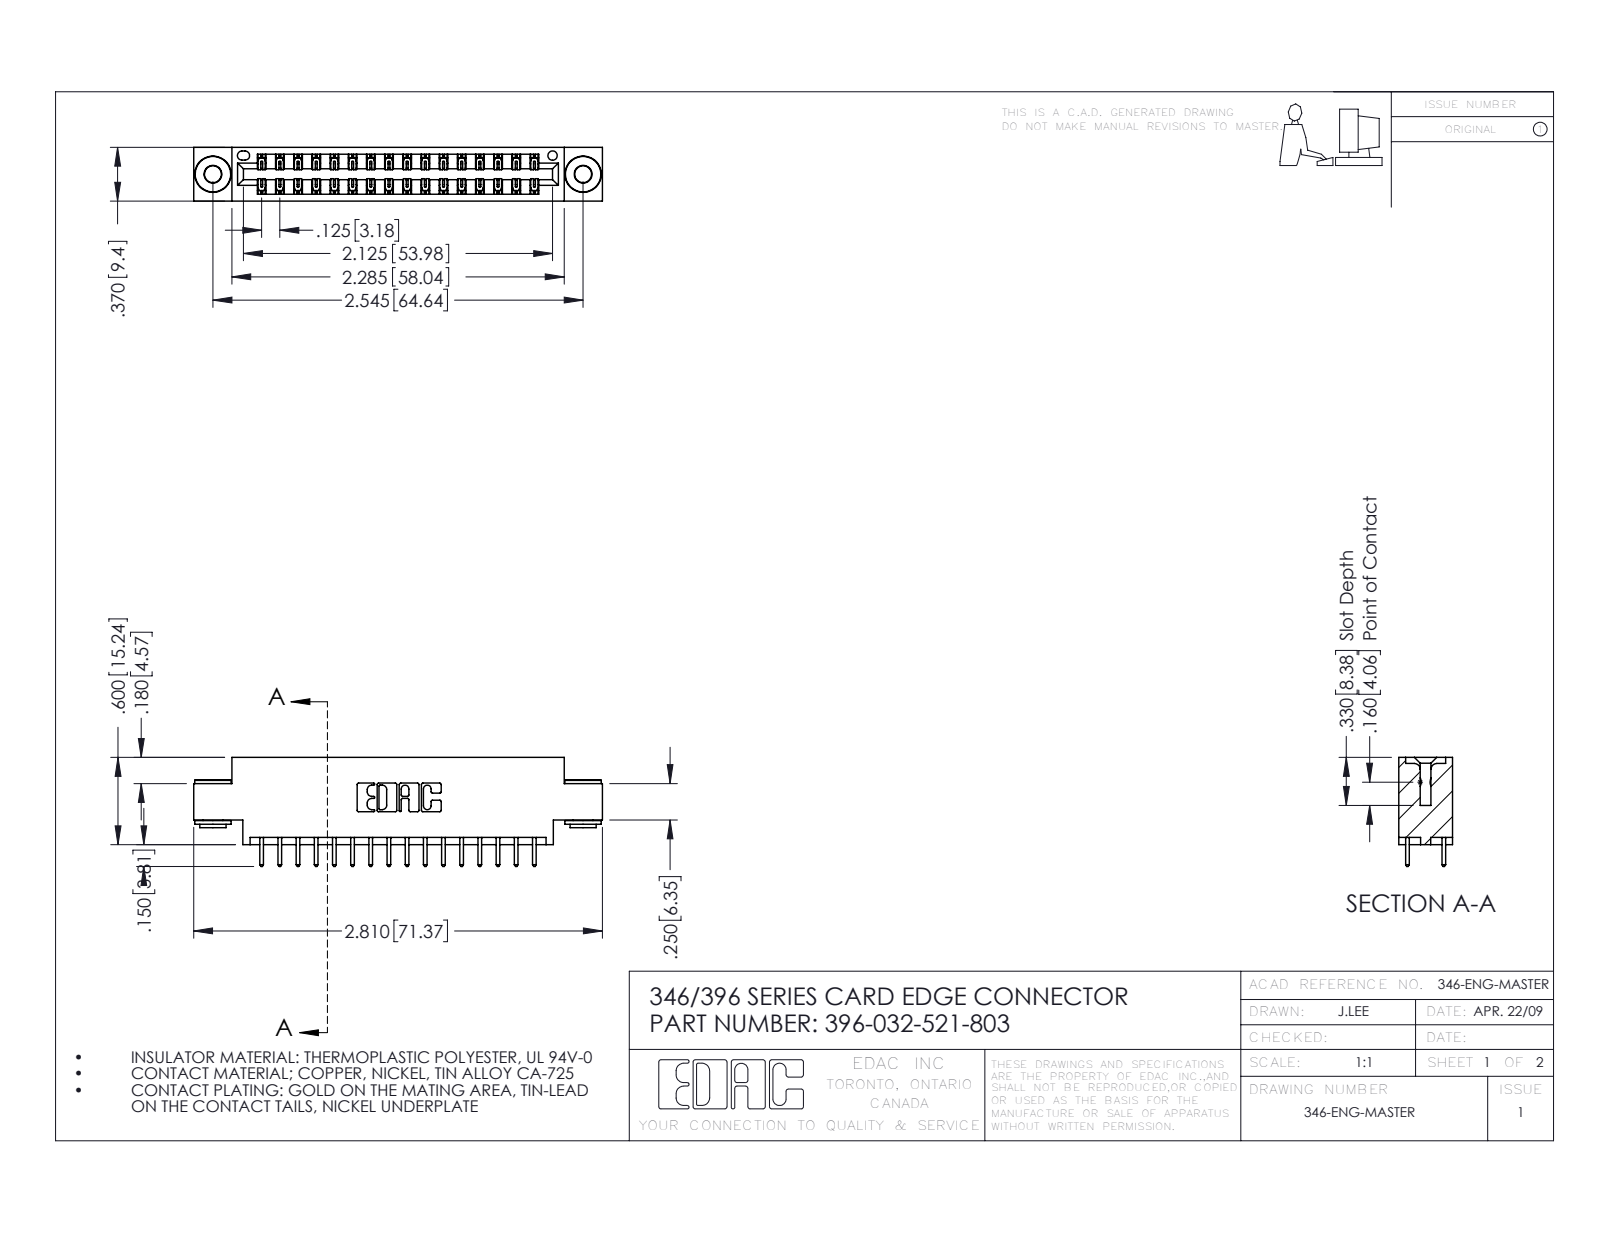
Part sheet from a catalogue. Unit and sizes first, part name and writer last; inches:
Units: inches
Overall size (bounding box): 2.81 × 0.75 × 0.37
Round holes (diameter × count): ⌀0.116 ×2, ⌀0.156 ×2, ⌀0.064 ×1
Round bosses / shafts (diameter × count): ⌀0.25 ×2, ⌀0.18 ×2, ⌀0.136 ×2
Partial cylindrical surfaces — rounded edges, fillets, slot ends (radius × count): R0.006 ×48, R0.01 ×32, R0.01 ×22, R0.007 ×6, R0.031 ×6, R0.026 ×3, R0.014 ×2, R0.022 ×2
Main face-to-face distances: 0.048, 0.322, 0.25, 0.37, 0.025, 0.072, 0.298, 0.275, 0.148, 0.222
Hole centre spacings: 0.246, 2.338, 2.545
Volume: 0.403 in³ · Surface area: 13.92 in²
Bodies: 35 solids, 1828 faces (1210 planar, 610 cylindrical, 8 other)
Part name (STEP PRODUCT): 396-032-521-803; 346 Part_0.170 Offset - 0.156 Dia-TH; 345-292-001_345-293-121; 345-250-002_345-250-002-102
STEP written by: SolidWorks 2016 (CONFIG_CONTROL_DESIGN)
